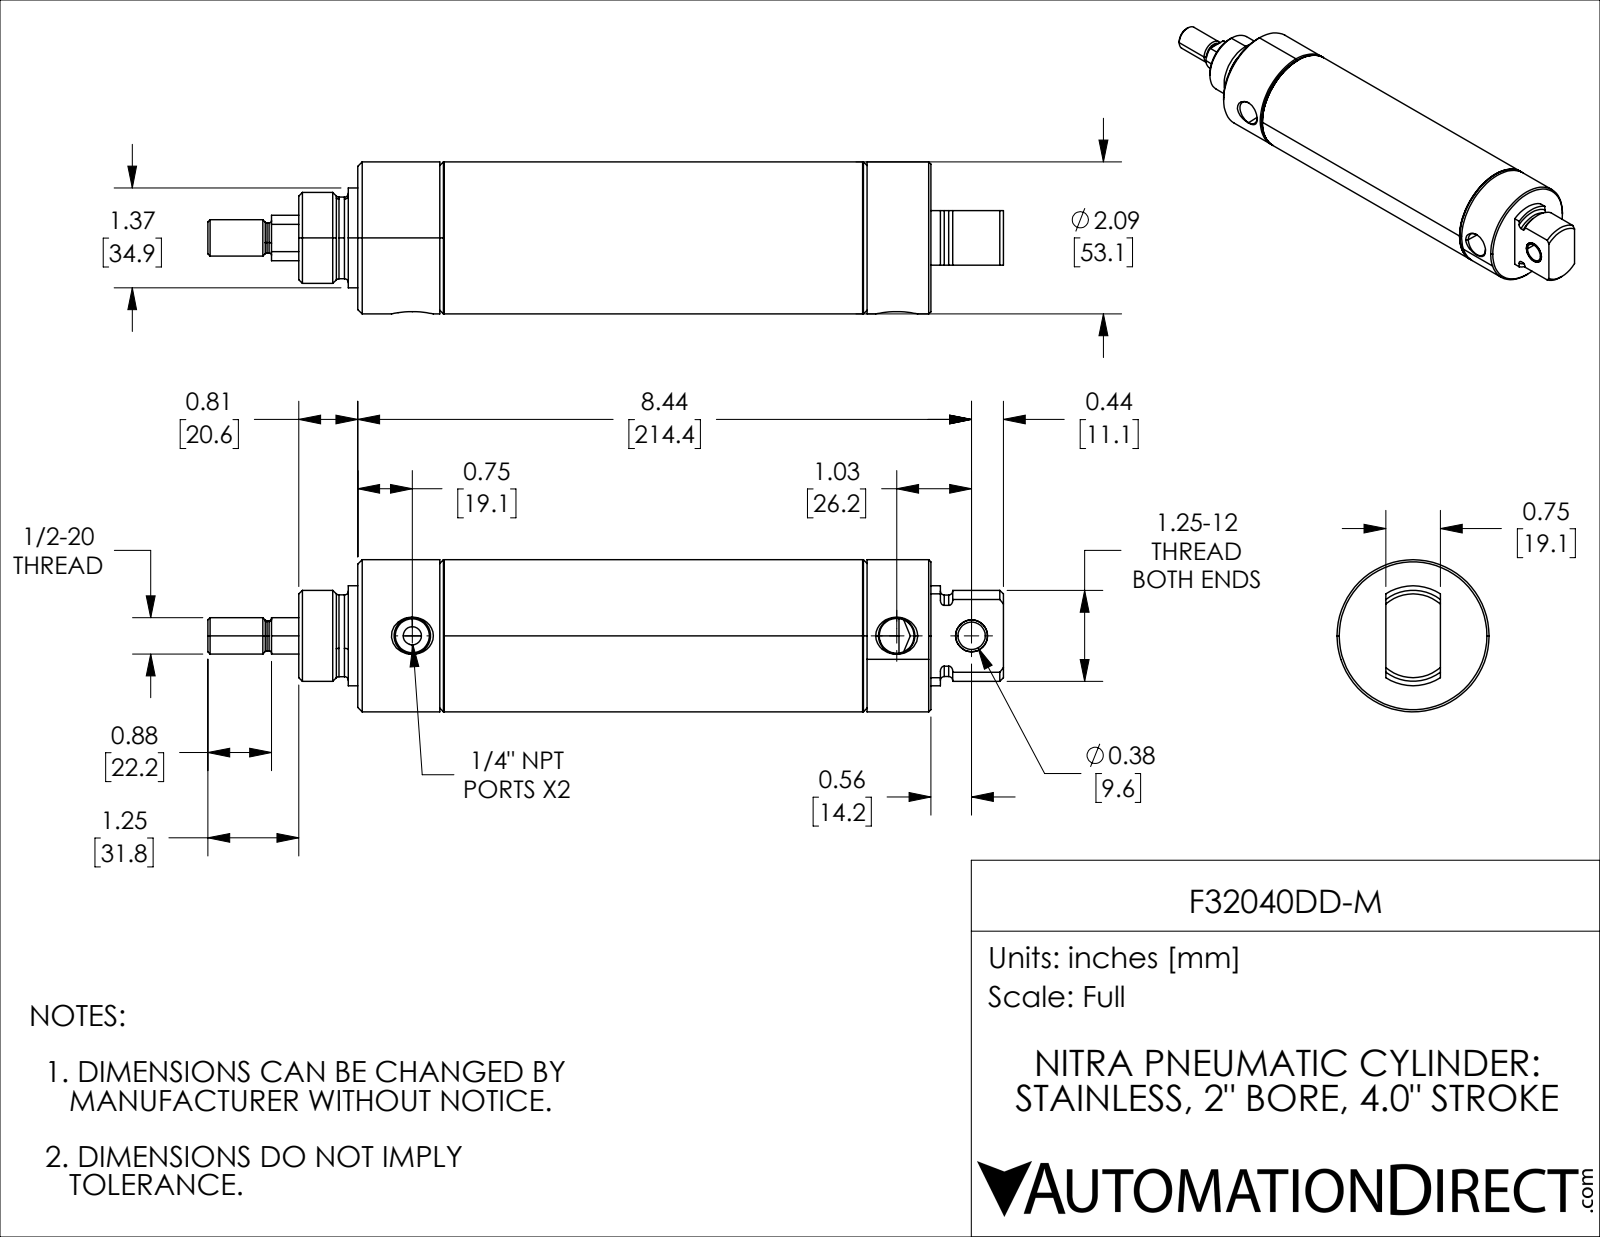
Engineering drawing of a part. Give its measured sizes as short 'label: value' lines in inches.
name: F32040DD-M_5; F32040DD-M_9; F32040DD-M; F32040DD-M_3 (+2 more)
written by: SolidWorks 2021 (CONFIG_CONTROL_DESIGN)
unit: in
bodies: 5 solids, 160 faces (31 planar, 60 cylindrical, 69 other)
size: 10.938 × 2.09 × 2.09
volume: 16.59 in³; area: 155.6 in²
holes: 1× ⌀0.25, 1× ⌀0.376, 1× ⌀0.439, 1× ⌀0.48, 1× ⌀0.65, 1× ⌀0.75, 1× ⌀1.931
bosses: 1× ⌀2.09, 1× ⌀2.014, 1× ⌀1.373, 1× ⌀1.25, 1× ⌀1.122, 1× ⌀0.625, 1× ⌀0.5, 1× ⌀0.412
rounds: 1× R0.561
face distances: 1.188, 4, 5.188, 6.378, 2.378, 1.19, 5.188, 1.188, 1.19, 1.502
hole spacings: 1.03, 6.66, 7.69
